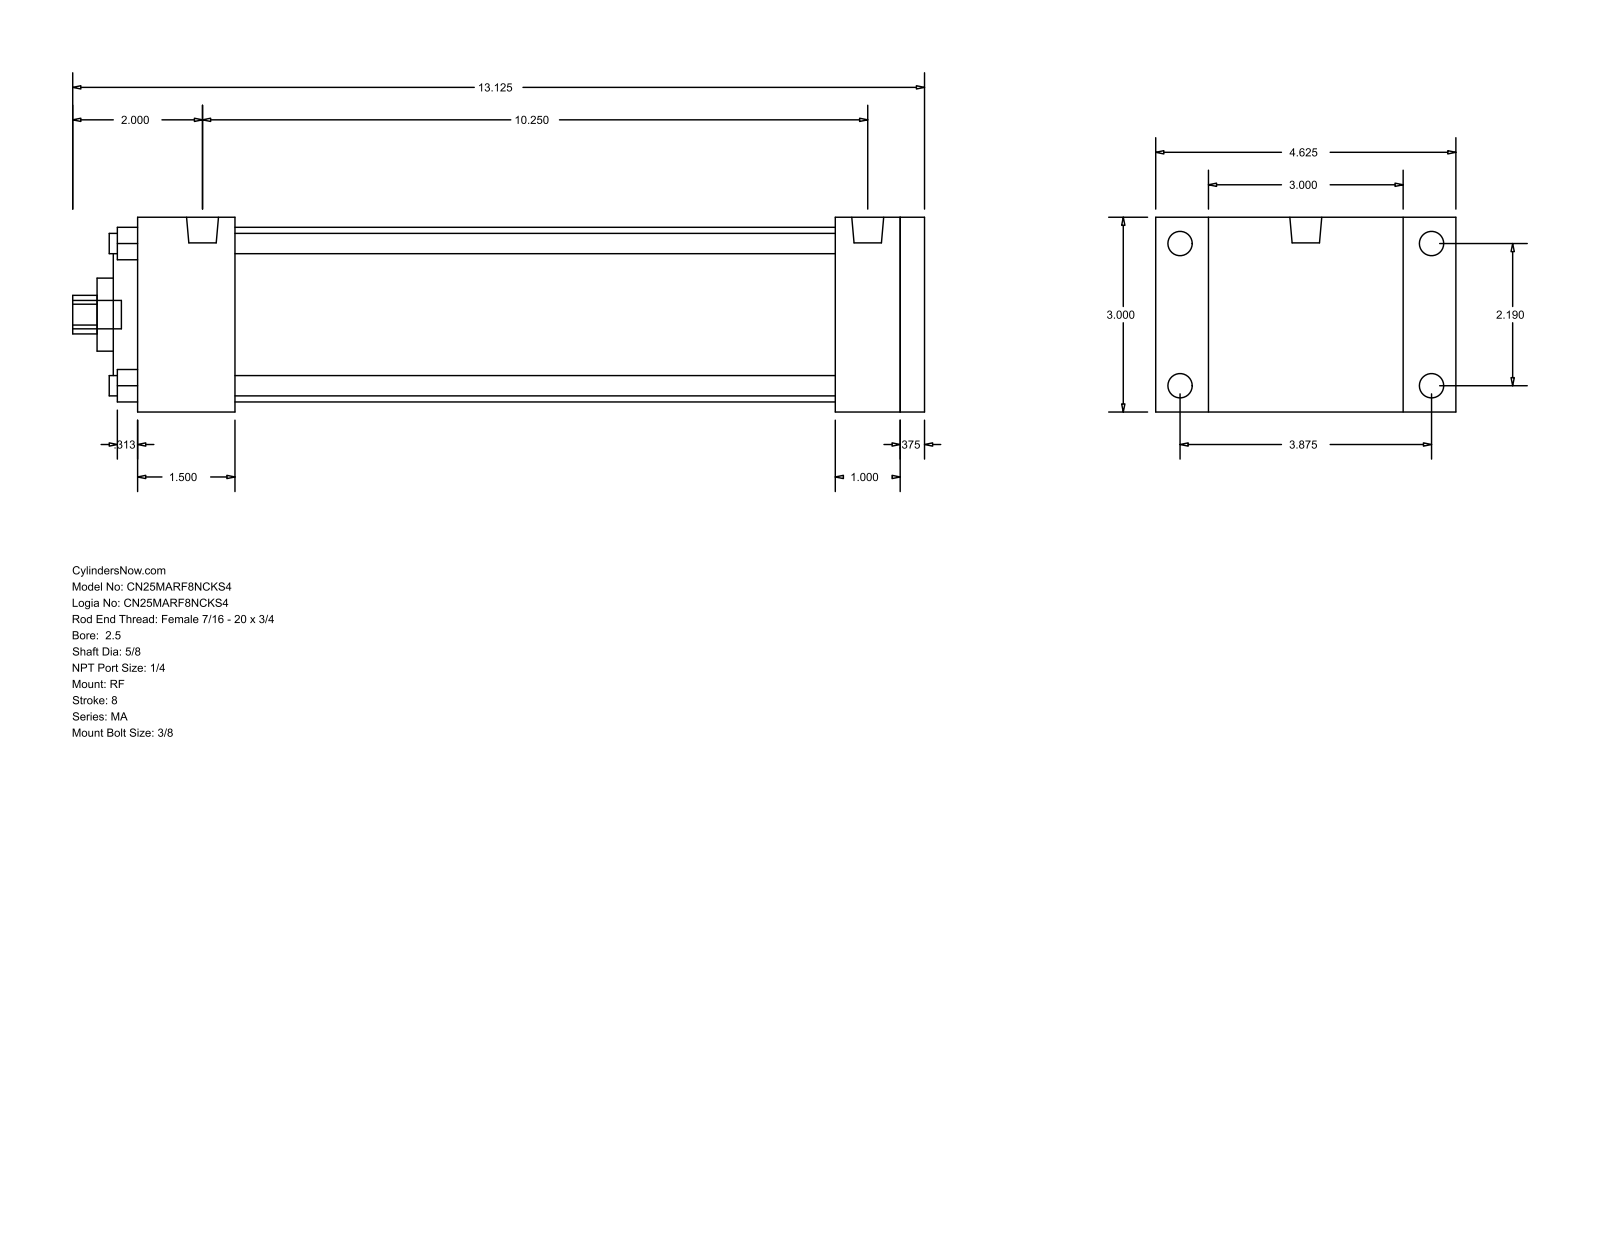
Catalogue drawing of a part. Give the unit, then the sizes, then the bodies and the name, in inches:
Units: inches
Overall size (bounding box): 13.125 × 4.625 × 3
Round holes (diameter × count): ⌀0.313 ×4, ⌀0.625 ×1, ⌀1.125 ×1, ⌀2 ×1, ⌀2.69 ×1
Round bosses / shafts (diameter × count): ⌀0.375 ×4, ⌀0.313 ×4, ⌀0.492 ×2, ⌀0.437 ×1
Partial cylindrical surfaces — rounded edges, fillets, slot ends (radius × count): R0.297 ×1
Main face-to-face distances: 3, 12.125, 0.375, 11.75, 1, 1.5, 10.75, 9.25, 10.25, 10.625
Hole centre spacings: 1.548, 2.19, 3.097
Bodies: 0 solids, 94 faces (65 planar, 29 cylindrical, 0 other)
Part name (STEP PRODUCT): MA_RF__0250_0.625
STEP written by: GSSL Pune (CONFIG_CONTROL_DESIGN)
